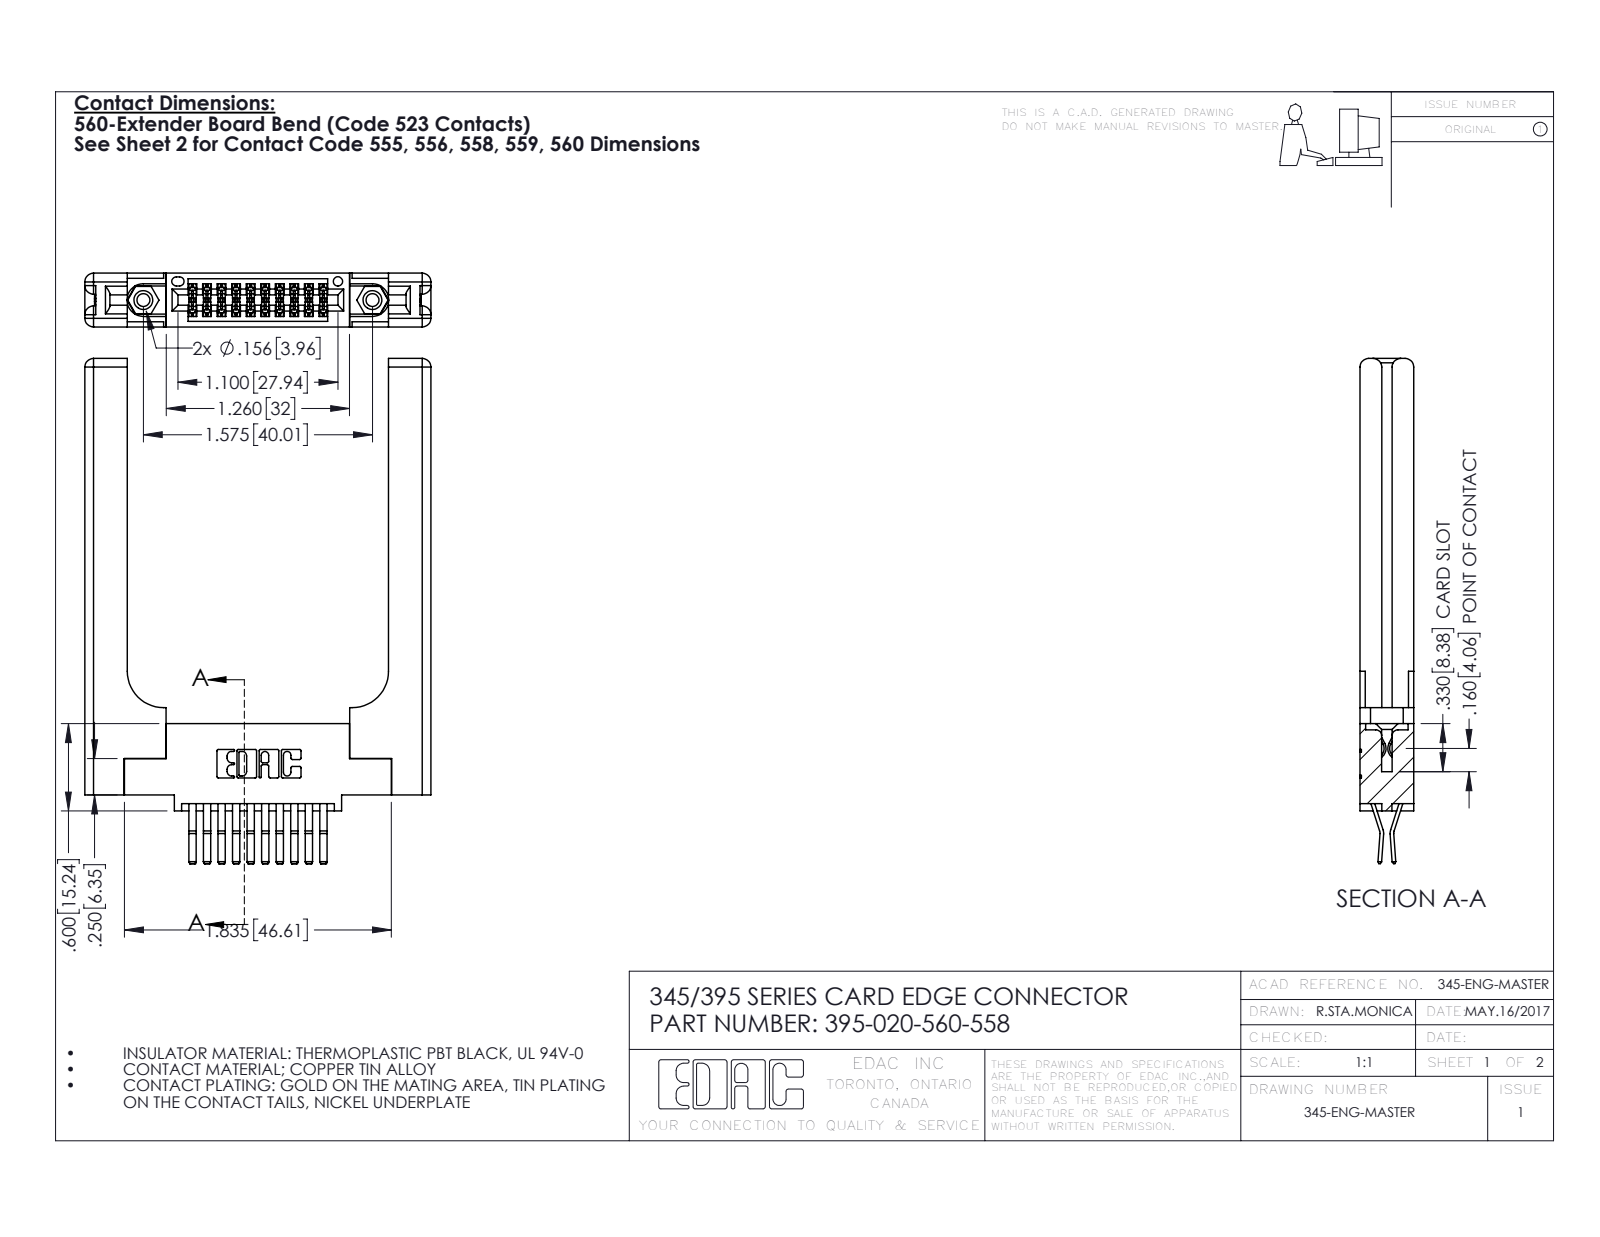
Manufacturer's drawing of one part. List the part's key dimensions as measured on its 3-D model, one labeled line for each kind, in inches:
Part name (STEP PRODUCT): 345-292-001_560 Tail; 395-020-560-558; 345 Part_0.110 Offset - 0.156 Dia-TH; 345-250-001_345-250-001-102 (+1 more)
STEP written by: SolidWorks 2016 (CONFIG_CONTROL_DESIGN)
Units: inches
Bodies: 25 solids, 1426 faces (892 planar, 474 cylindrical, 60 other)
Overall size (bounding box): 3.472 × 2.379 × 0.37
Volume: 0.861 in³ · Surface area: 20.45 in²
Round holes (diameter × count): ⌀0.089 ×2, ⌀0.125 ×2, ⌀0.156 ×2, ⌀0.064 ×1
Round bosses / shafts (diameter × count): ⌀0.155 ×2
Partial cylindrical surfaces — rounded edges, fillets, slot ends (radius × count): R0.006 ×30, R0.01 ×22, R0.06 ×16, R0.007 ×6, R0.031 ×6, R0.026 ×3, R0.01 ×2, R0.014 ×2
Main face-to-face distances: 0.37, 0.072, 0.15, 0.22, 0.077, 0.148, 0.298, 0.025, 1.796, 0.225
Hole centre spacings: 0.27, 1.344, 1.575
